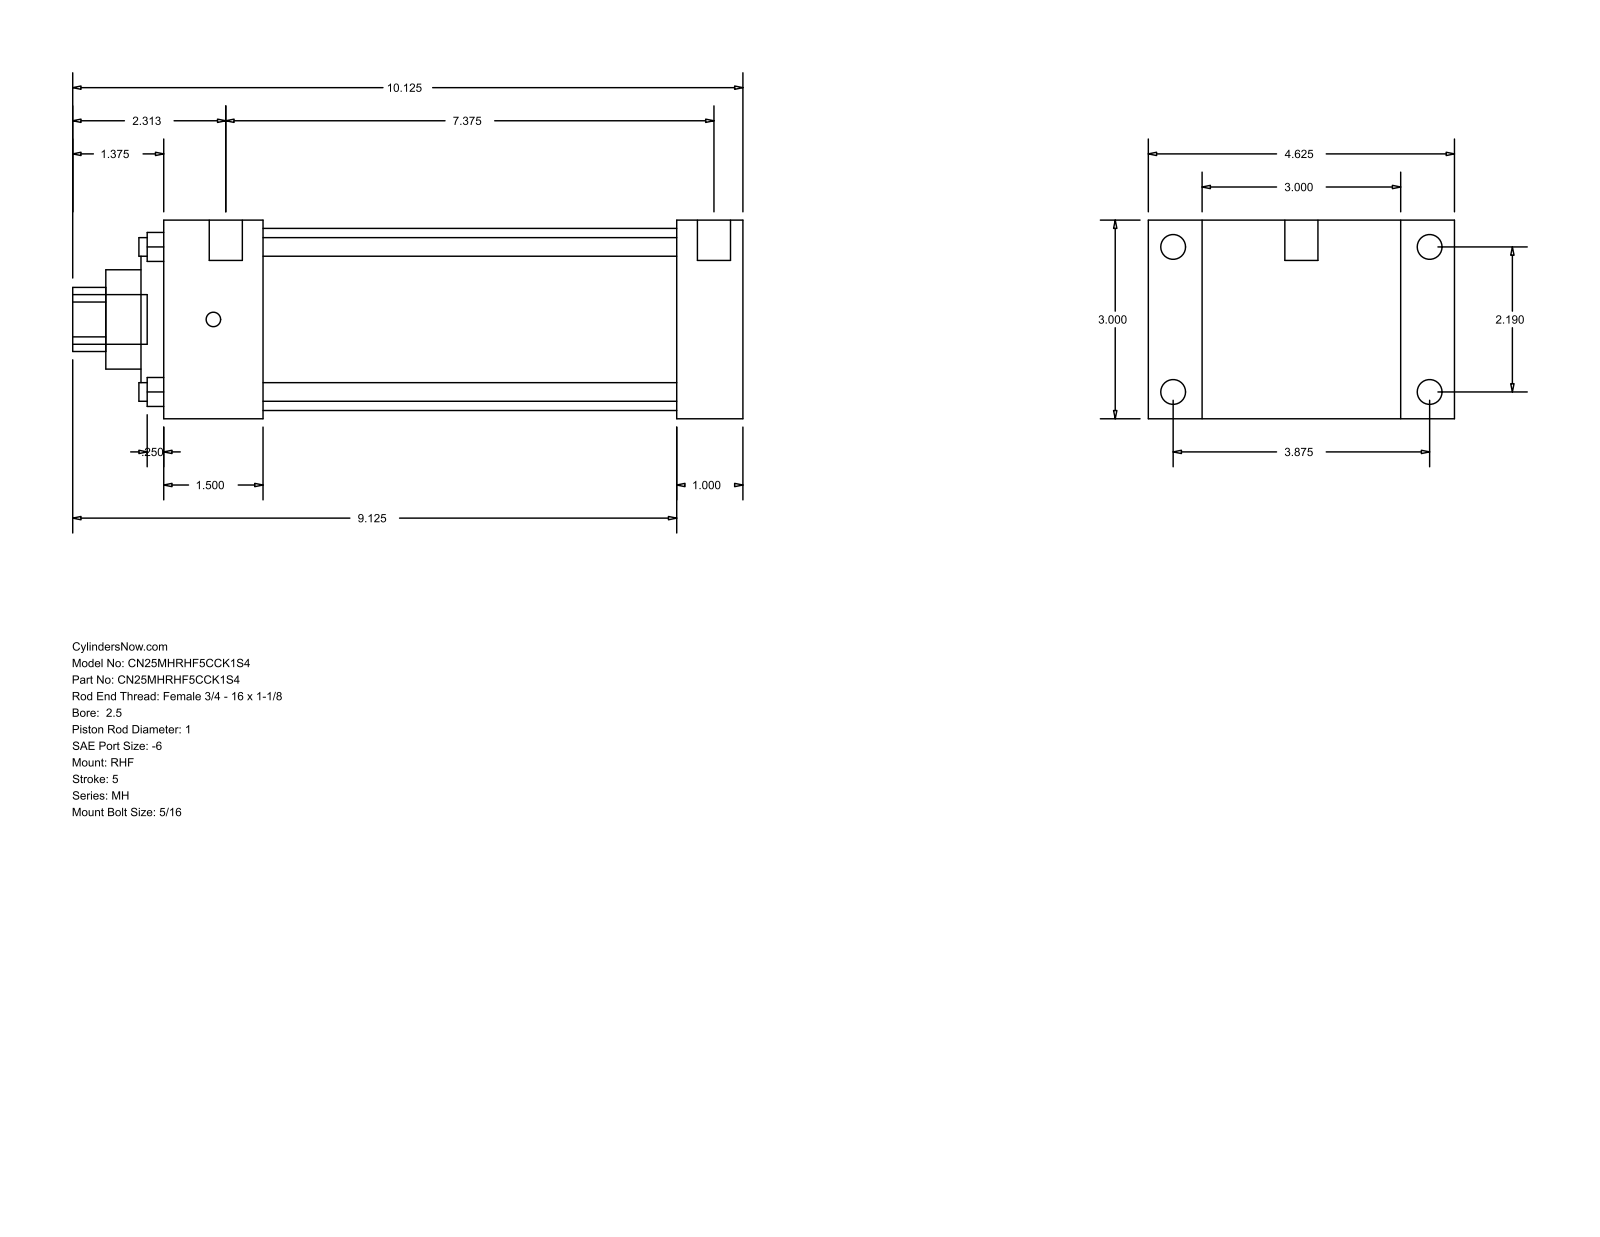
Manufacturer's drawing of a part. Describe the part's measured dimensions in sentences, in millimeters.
The part is named "MH_RHF__0250_1". Its 3-D file was written by "GSSL Pune (CONFIG_CONTROL_DESIGN)". It is 0 solids with 90 faces: 61 planar, 29 cylindrical and 0 other. Overall it measures 257.18 by 117.47 by 76.2 millimeters. Round holes: 4 of diameter 7.14, 1 of diameter 25.4, 1 of diameter 38.1, 1 of diameter 60.33, 1 of diameter 69.85. Round bosses or shafts: 4 of diameter 9.53, 4 of diameter 5.56, 2 of diameter 12.7, 1 of diameter 19.05. Partial cylindrical surfaces (rounded edges, fillets, slot ends): 1 of radius 12.29. The main face-to-face distances are 76.2, 25.4, 20.64, 96.84, 196.86, 222.26, 117.48, 38.11, 158.75, 184.15. The hole center spacings are 39.33, 55.62, 78.66.
